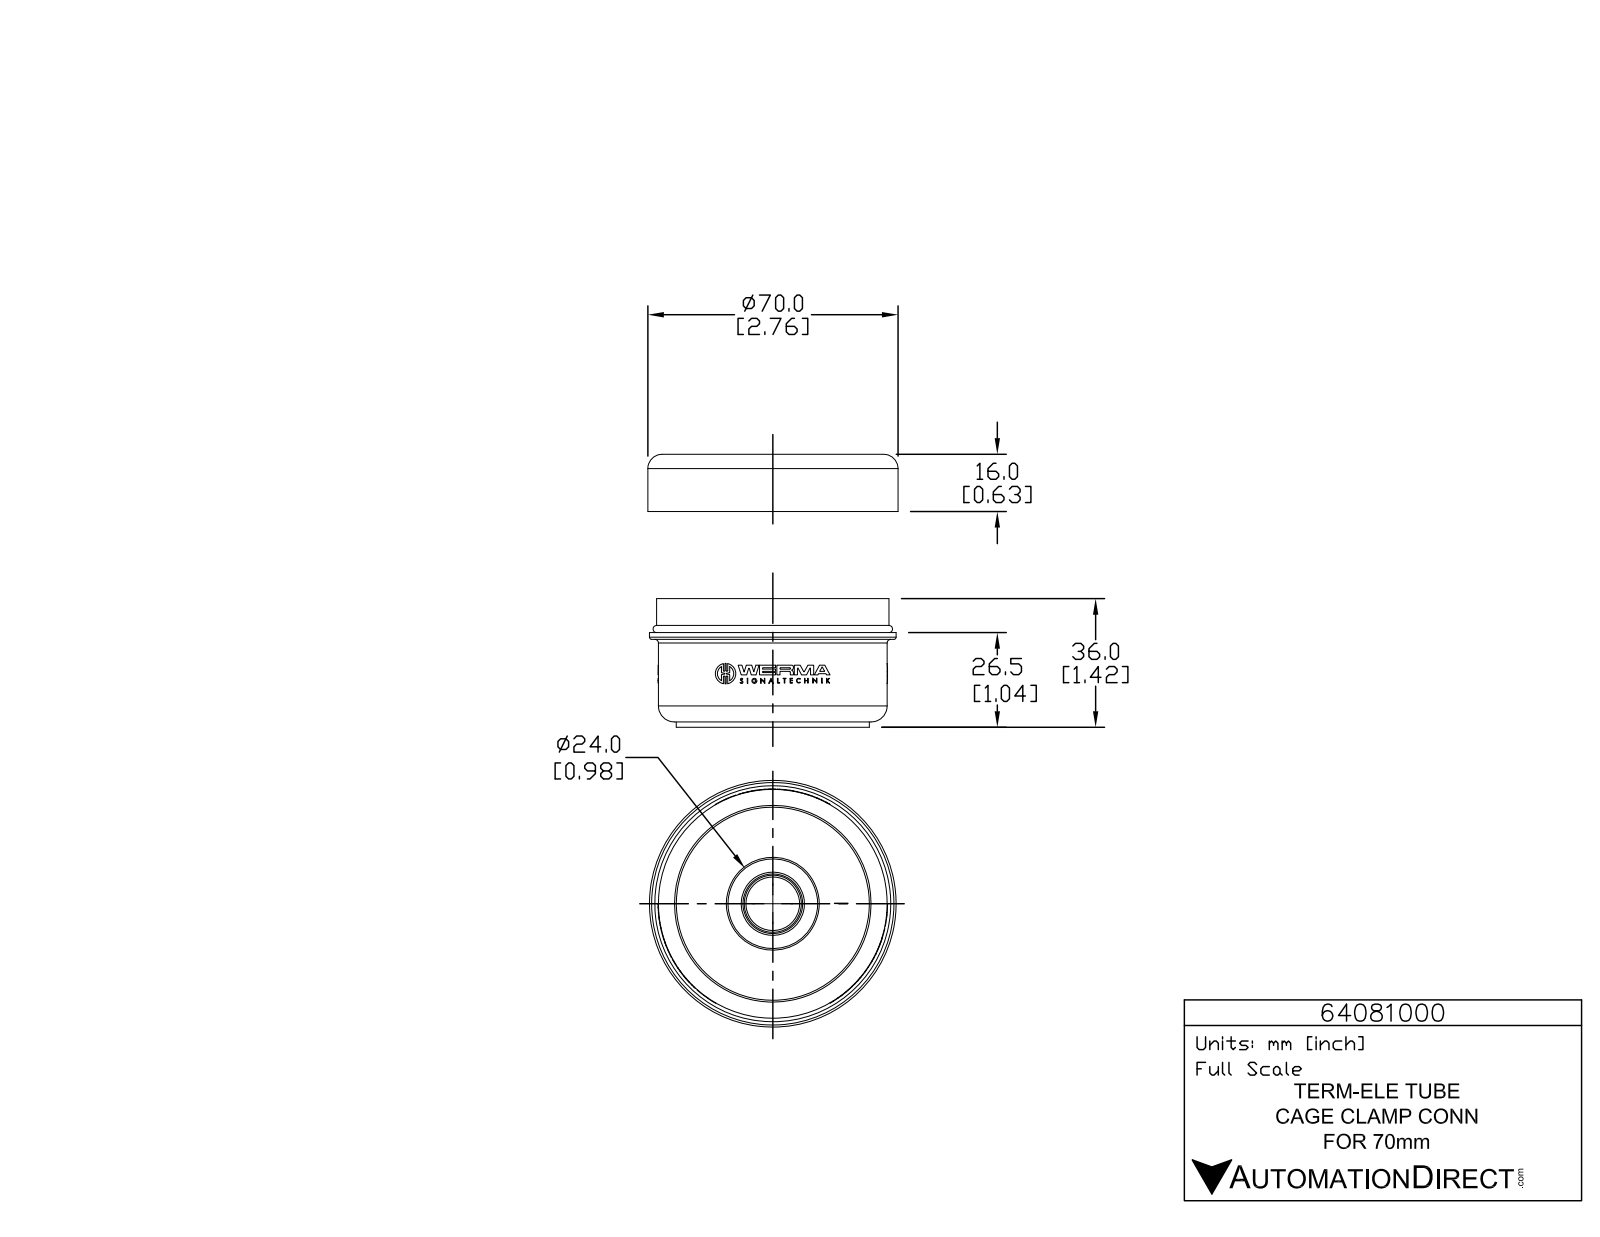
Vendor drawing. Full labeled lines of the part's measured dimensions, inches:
Part name (STEP PRODUCT): 64081000
STEP written by: SolidWorks 2015 (AUTOMOTIVE_DESIGN)
Units: inches
Bodies: 2 solids, 1069 faces (732 planar, 315 cylindrical, 22 other)
Overall size (bounding box): 2.756 × 2.756 × 1.732
Volume: 7.073 in³ · Surface area: 52.18 in²
Round holes (diameter × count): ⌀0.039 ×3, ⌀0.236 ×2, ⌀0.099 ×1, ⌀0.169 ×1, ⌀0.395 ×1, ⌀0.591 ×1, ⌀0.988 ×1, ⌀1.024 ×1, ⌀2.661 ×1, ⌀2.701 ×1
Round bosses / shafts (diameter × count): ⌀0.226 ×3, ⌀0.056 ×3, ⌀2.756 ×1, ⌀2.717 ×1, ⌀2.559 ×1, ⌀2.52 ×1, ⌀2.126 ×1, ⌀0.697 ×1
Partial cylindrical surfaces — rounded edges, fillets, slot ends (radius × count): R0.008 ×6, R0.008 ×6, R0.008 ×6, R0.131 ×6, R0.004 ×3, R0.005 ×3, R0.006 ×3, R0.008 ×3
Main face-to-face distances: 0.177, 0.079, 0.256, 1.476, 1.654, 1.732, 1.102, 0.374, 0.551, 0.63
Hole centre spacings: 0.827, 0.02, 0.104, 0.388, 0.472, 0.572, 0.846, 0.917
